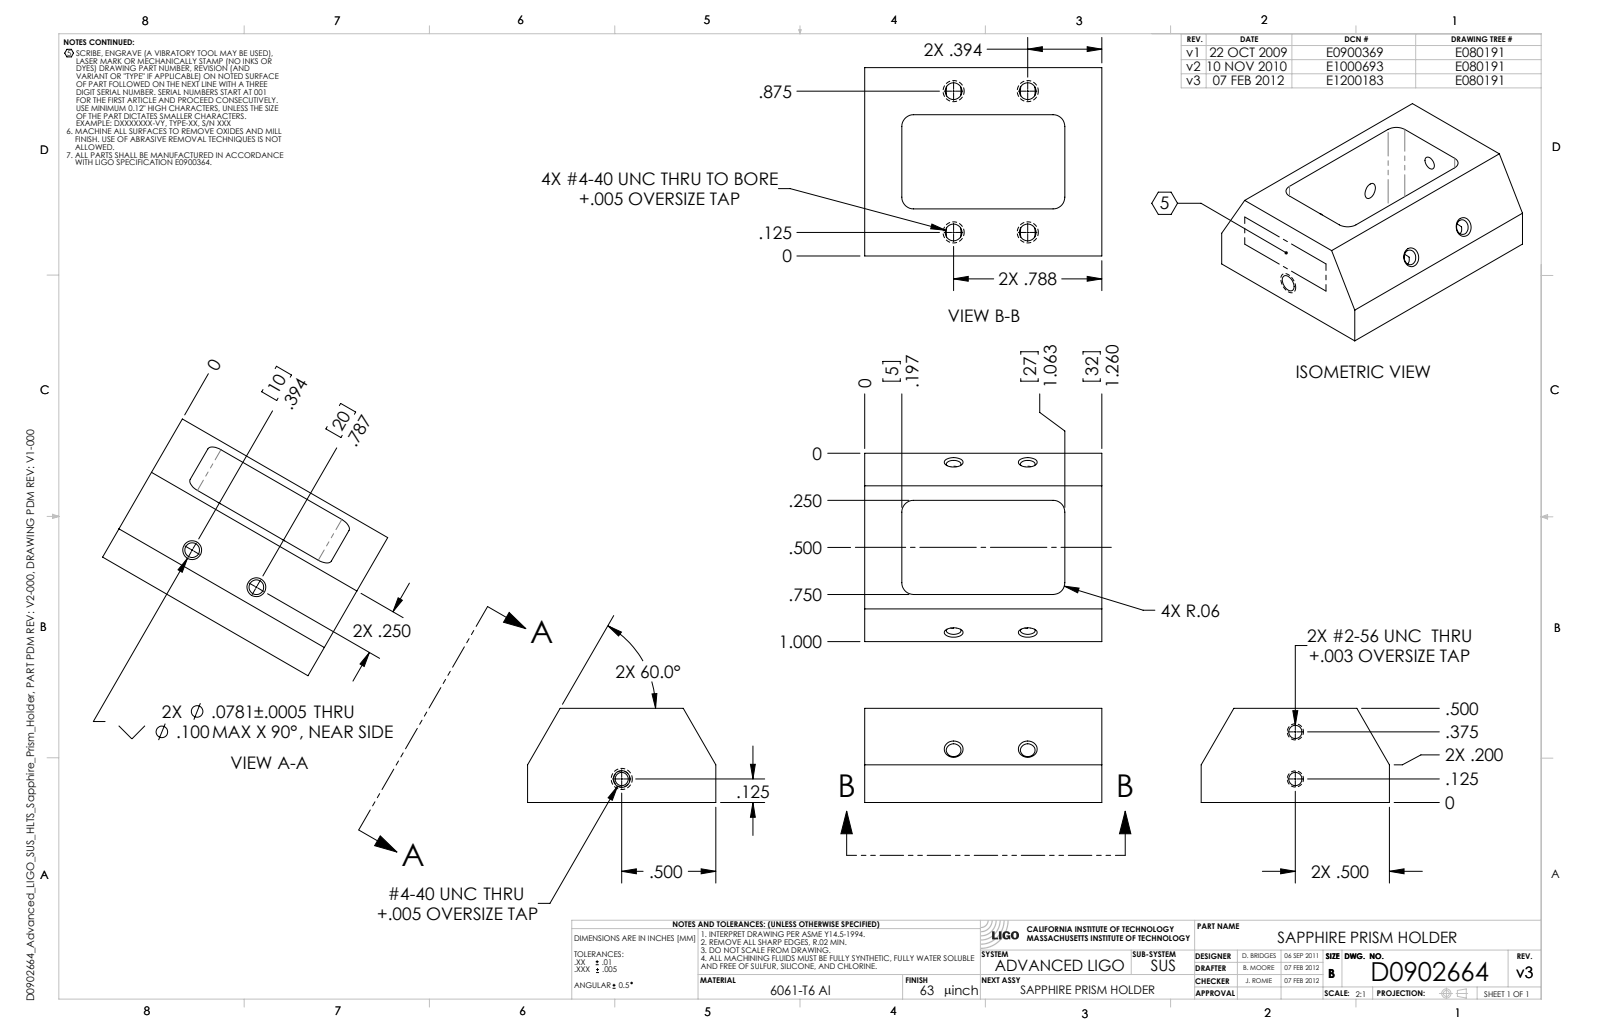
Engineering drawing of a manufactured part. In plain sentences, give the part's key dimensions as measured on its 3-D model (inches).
The part is named "D0902664-v3". Its 3-D file was written by "SolidWorks 2012 (CONFIG_CONTROL_DESIGN)". It is 1 solid with 54 faces: 20 planar, 26 cylindrical and 8 other. Overall it measures 1.26 by 1 by 0.5 inches. Its volume is 0.337 cubic inches and its surface area 5.285 square inches. Round holes: 5 of diameter 0.089, 4 of diameter 0.078, 2 of diameter 0.07. Partial cylindrical surfaces (rounded edges, fillets, slot ends): 2 of radius 0.062, 2 of radius 0.063. The main face-to-face distances are 0.5, 0.25, 0.75, 1.26, 0.197, 1.063, 1, 0.866, 0.239, 0.261. The hole center spacings are 0.394, 0.394, 0.75, 0.847, 0.25.
